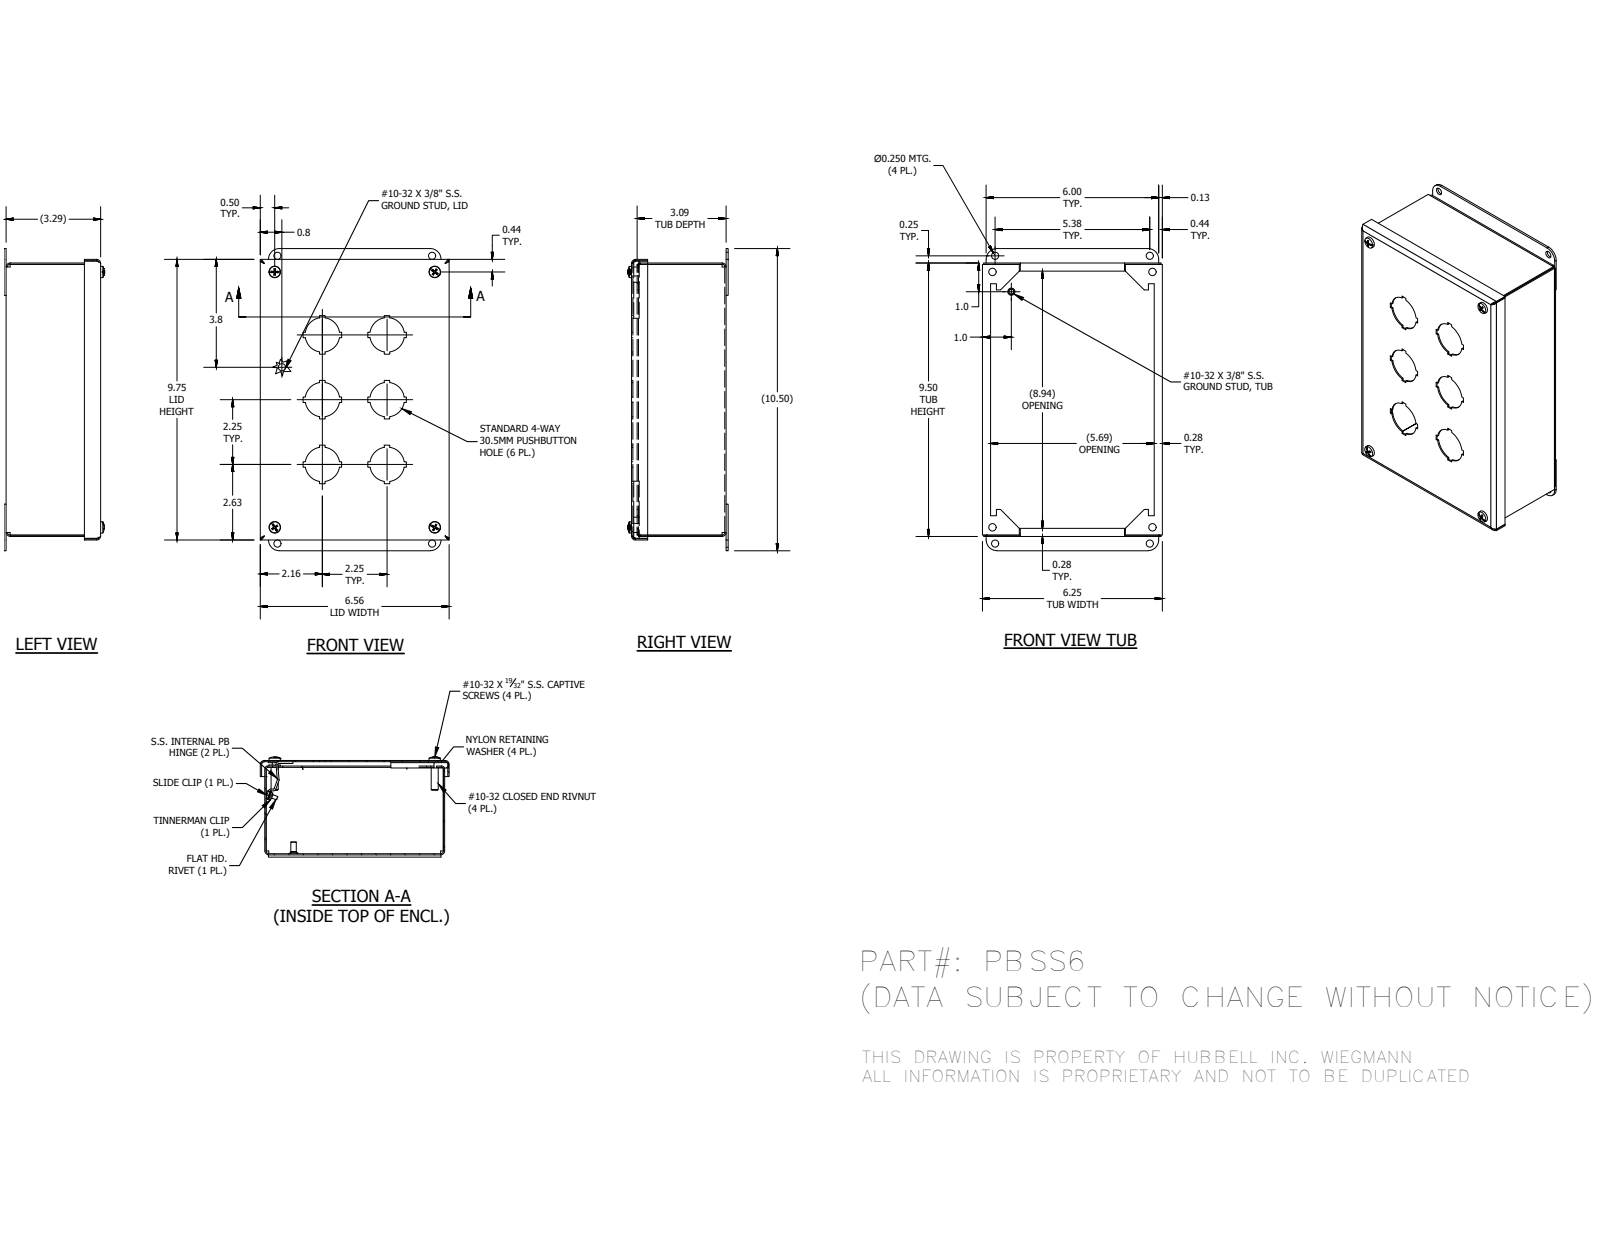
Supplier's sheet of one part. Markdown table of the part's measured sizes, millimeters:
| quantity | value |
| --- | --- |
| part name | PBSS6LID; 37210; 39077; PBSS6BKP (+8 more) |
| STEP written by | Autodesk Inventor 2016 (AUTOMOTIVE_DESIGN) |
| units | millimeters |
| bodies | 25 solids, 735 faces (473 planar, 154 cylindrical, 108 other) |
| overall size | 266.7 × 166.69 × 88.41 |
| volume | 215 280 mm³ |
| surface area | 349 708 mm² |
| round holes (diameter × count) | 30.48 × 6, 3.96 × 4, 4.98 × 4, 6.35 × 4, 6.53 × 4, 7.06 × 4, 7.14 × 4, 3.38 × 2, 3.56 × 2, 7.95 × 2 |
| round bosses / shafts (diameter × count) | 11.51 × 4, 10.31 × 4, 6.3 × 4, 4.25 × 4, 6.35 × 3, 4.83 × 2, 3.17 × 1 |
| partial cylindrical surfaces (radius × count) | 2.38 × 8, 3.52 × 8, 4.78 × 6, 1.59 × 4, 2.27 × 4, 2.29 × 4, 2.73 × 4, 9.53 × 4 |
| main face-to-face distances | 1.14, 1.15, 81.15, 82.3, 82.29, 83.44, 240.16, 157.6, 158.75, 156.46 |
| hole center spacings | 57.15, 80.34, 80.82, 133.06, 174.99, 188.38, 239.72, 0.48 |
